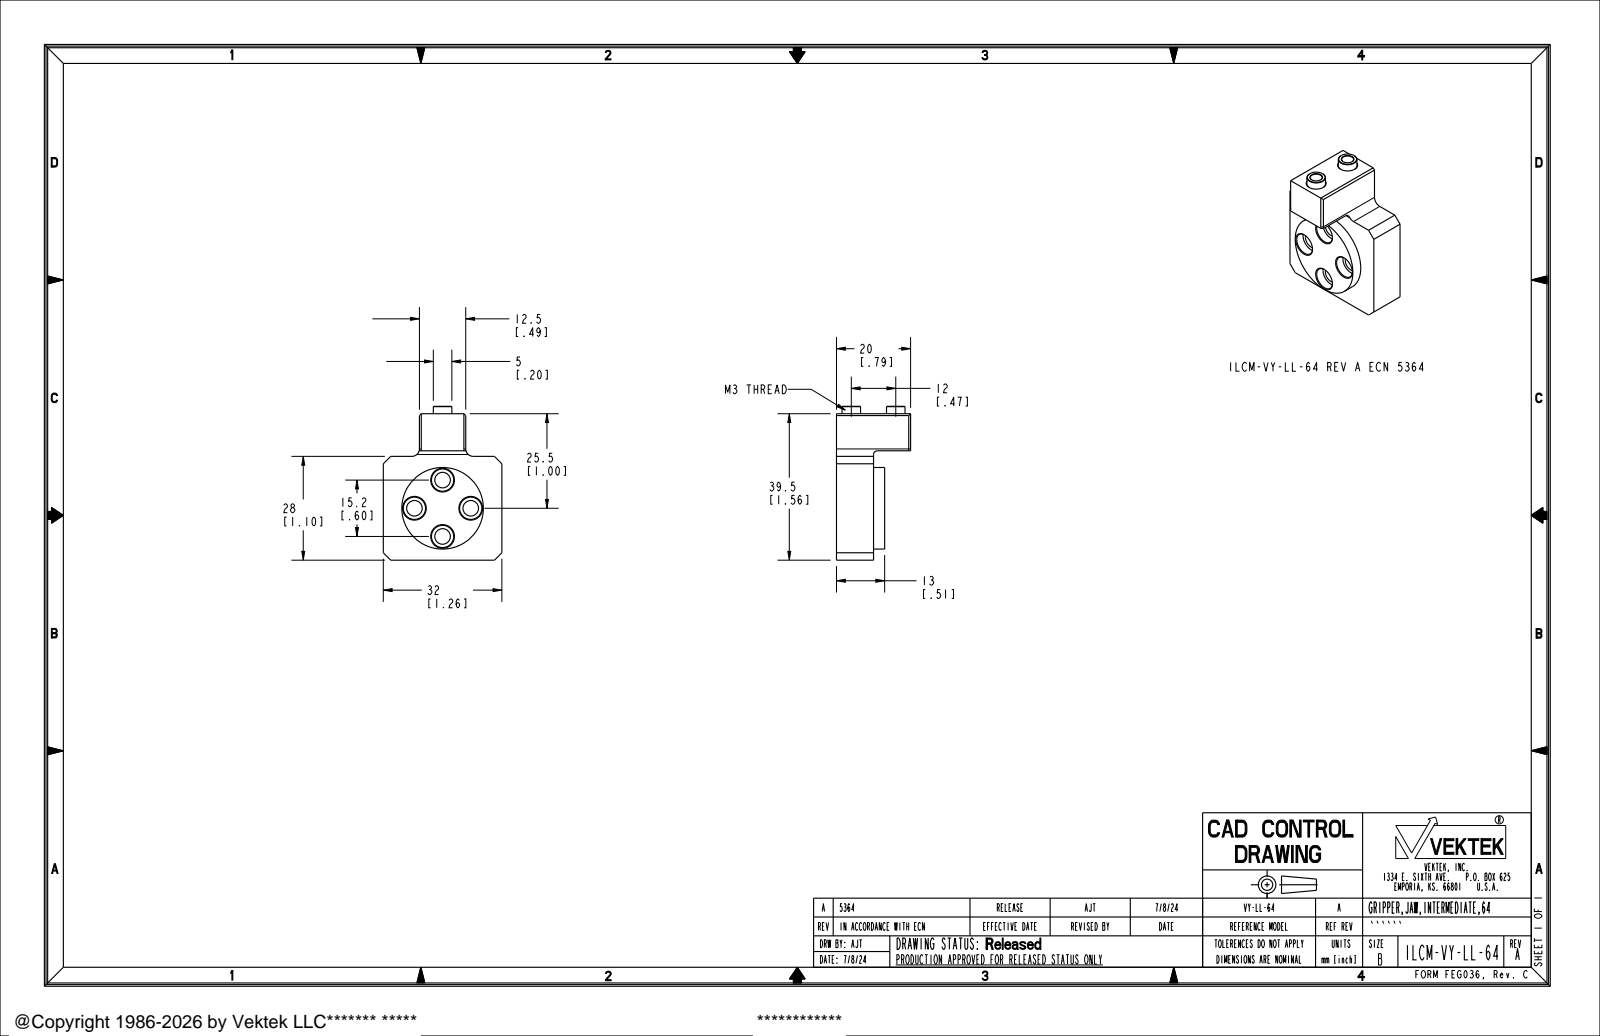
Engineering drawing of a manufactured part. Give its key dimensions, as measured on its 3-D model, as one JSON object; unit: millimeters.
{"part_name": "TY-LL-64_1; BOCCOLA_5H7L4_4; TY-LL-64; ILCM-VY-LL-64", "step_written_by": "CREO PARAMETRIC BY PTC INC, 2021164 (AUTOMOTIVE_DESIGN)", "units": "millimeters", "bodies": {"solids": 3, "faces": 114, "planar": 35, "cylindrical": 45, "other": 34}, "overall_size": [41.5, 32, 20], "volume_mm3": 11100, "surface_area_mm2": 5359, "round_holes": [[4.2, 4], [6, 4], [8, 4], [2.5, 2], [3.2, 2], [5, 2]], "round_bosses_or_shafts": [[22, 1]], "partial_cylinders_radius": [[2, 2], [1, 1]], "face_to_face_distances": [10, 9.8, 22.3, 5, 13, 3, 32, 39.5, 12.5, 8], "hole_center_spacings": [10.7, 15.2, 12]}
